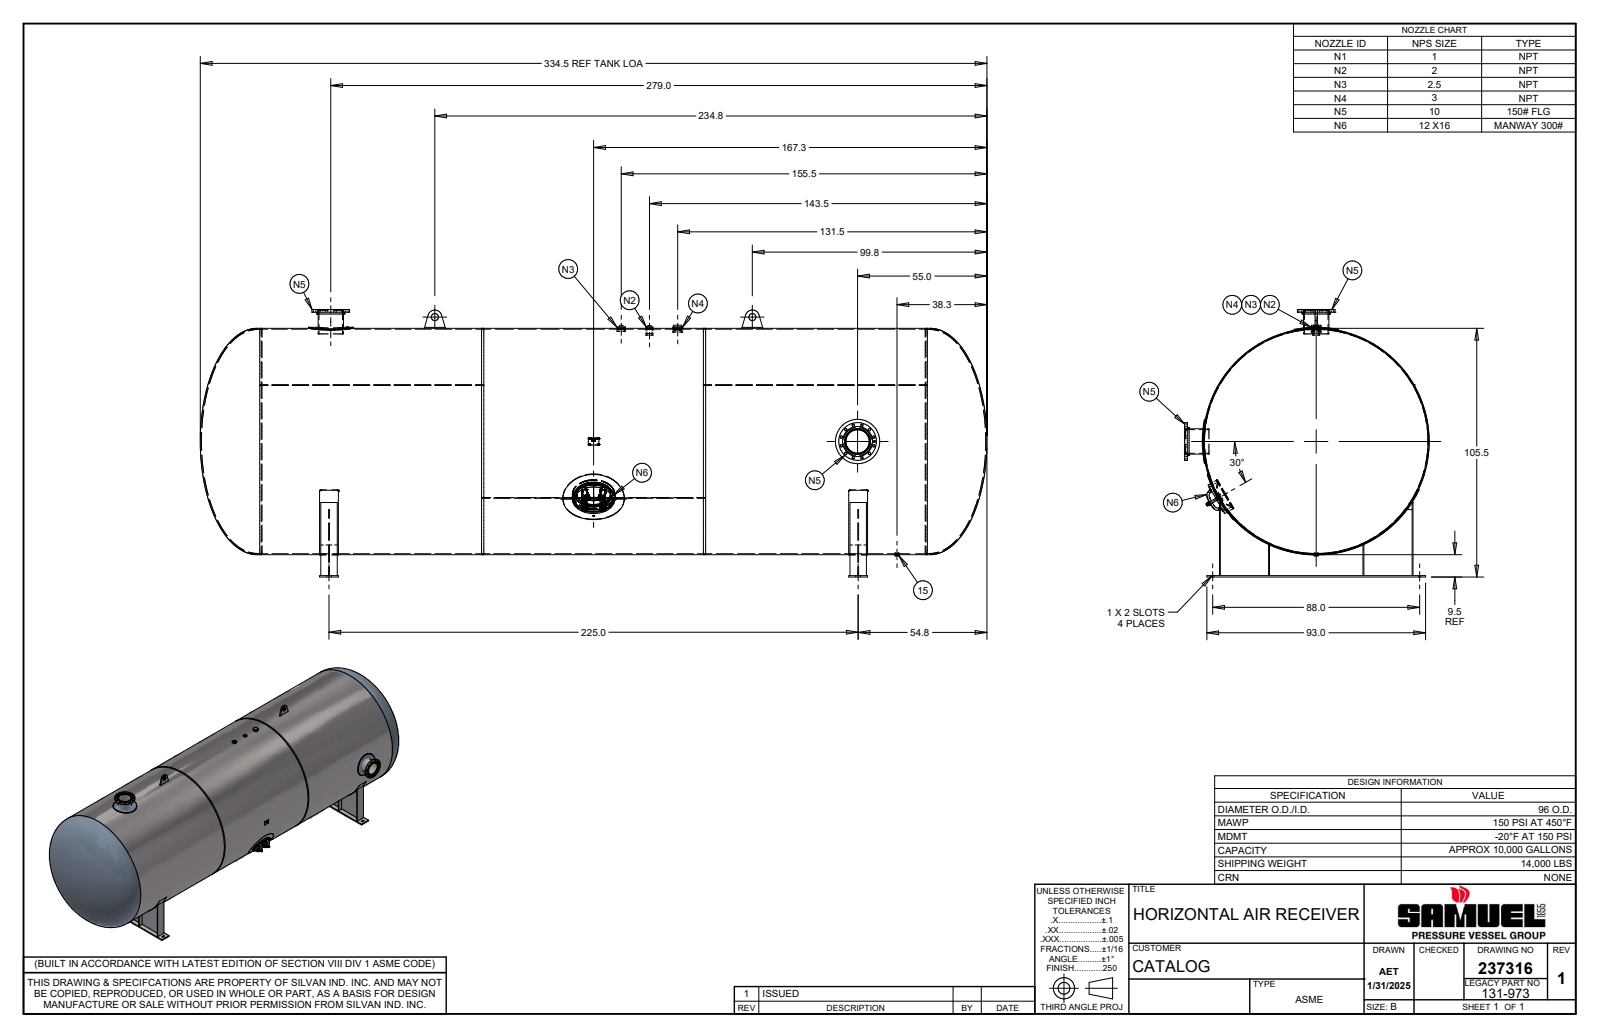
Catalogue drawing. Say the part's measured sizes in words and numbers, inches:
The part is named "237316; 131-973SF-SL1; 131-973SF-SL2; 131-973SF-SL3 (+8 more)". Its 3-D file was written by "Autodesk Inventor 2022 (AUTOMOTIVE_DESIGN)". It is 49 solids with 1038 faces: 534 planar, 213 cylindrical and 291 other. Overall it measures 334.5 by 113.5 by 104 inches. Its volume is 46 763 cubic inches and its surface area 234 243 square inches. Round holes: 25 of diameter 1, 3 of diameter 3, 2 of diameter 0.42, 2 of diameter 0.865, 2 of diameter 1.125, 2 of diameter 10, 2 of diameter 10.02, 2 of diameter 10.7, 2 of diameter 10.88, 1 of diameter 0.422, 1 of diameter 1.193, 1 of diameter 2. Round bosses or shafts: 2 of diameter 18.813, 2 of diameter 16, 2 of diameter 12.75, 2 of diameter 12, 2 of diameter 10.75, 2 of diameter 1, 1 of diameter 96, 1 of diameter 4.25. Partial cylindrical surfaces (rounded edges, fillets, slot ends): 16 of radius 0.5, 12 of radius 0.776, 6 of radius 0.375, 6 of radius 1, 5 of radius 3, 4 of radius 0.75, 4 of radius 1.156, 3 of radius 2.776. The main face-to-face distances are 225, 0.375, 0.625, 225.375, 224.625, 0.375, 81.937, 20.906, 61.031, 81.562. The hole center spacings are 7.125, 3.688, 10.076, 12.341, 13.765, 14.25, 1.848, 5.407.
